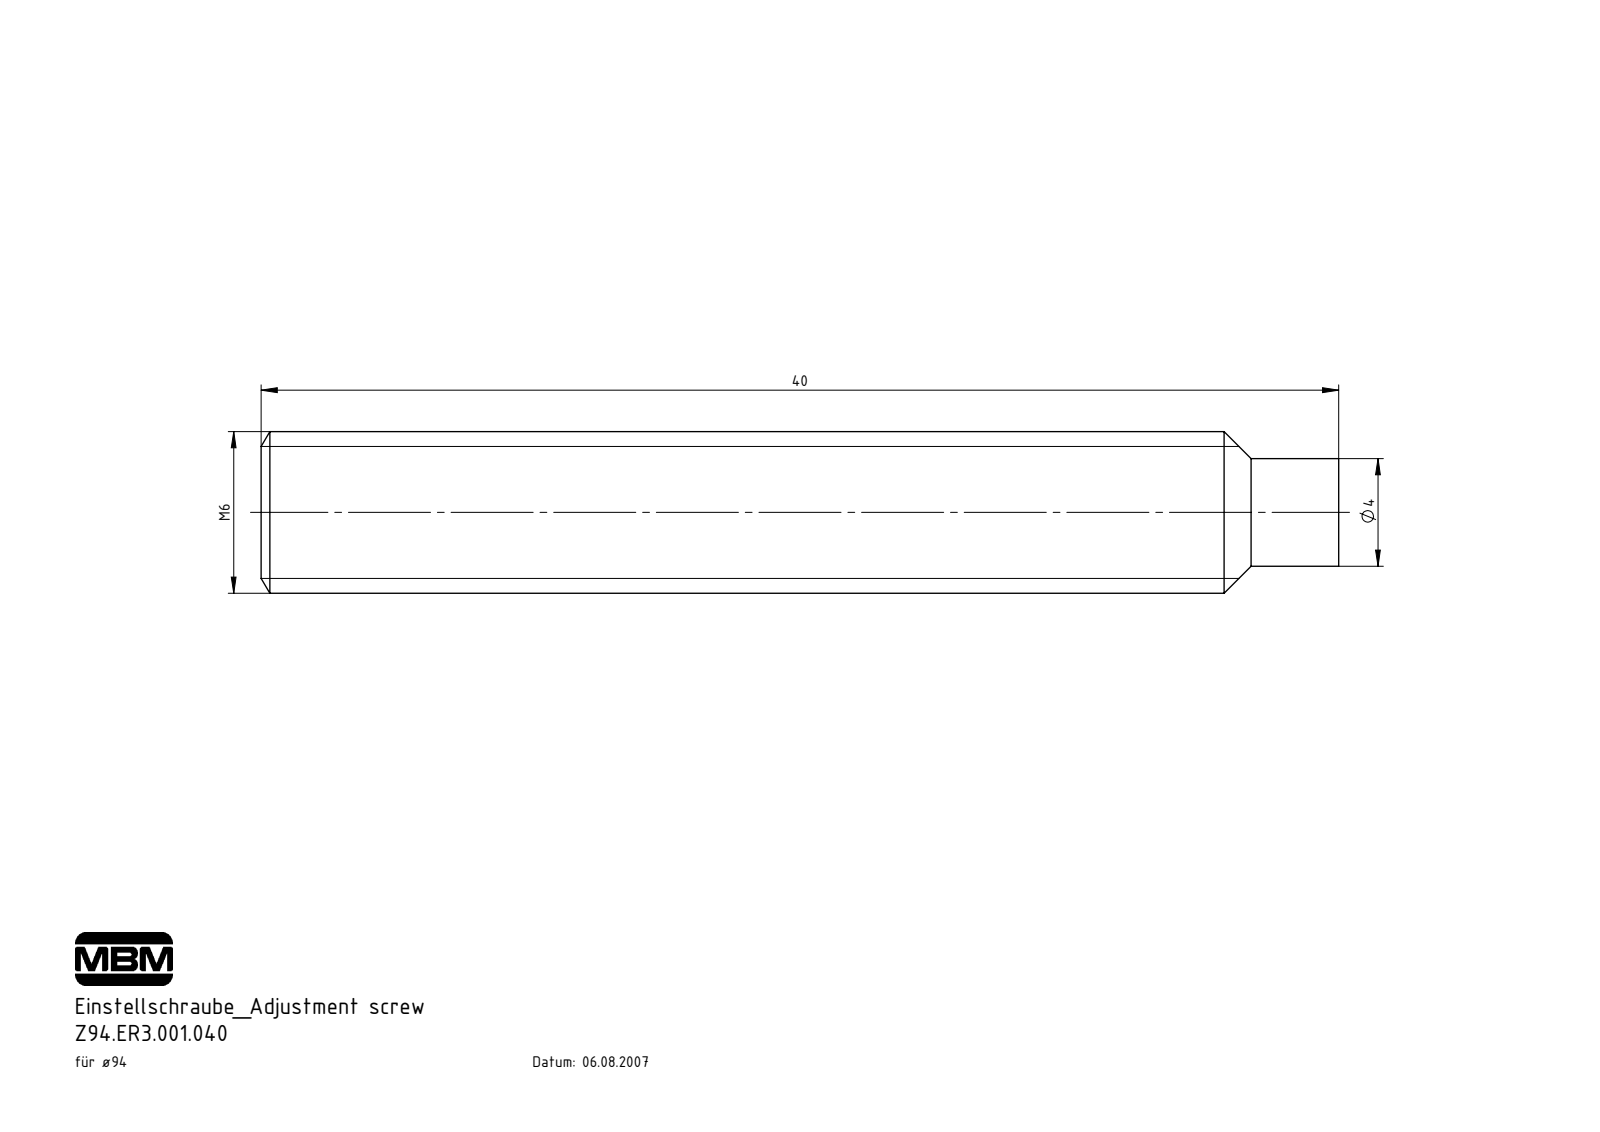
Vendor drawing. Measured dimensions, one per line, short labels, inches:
name: Z94.ER3.001.040
written by: SolidWorks 2017 (AUTOMOTIVE_DESIGN)
unit: in
bodies: 1 solid, 17 faces (9 planar, 4 cylindrical, 4 other)
size: 1.575 × 0.236 × 0.236
volume: 0.064 in³; area: 1.26 in²
bosses: 1× ⌀0.236, 1× ⌀0.157
face distances: 0.118, 1.575, 0.138, 1.437
